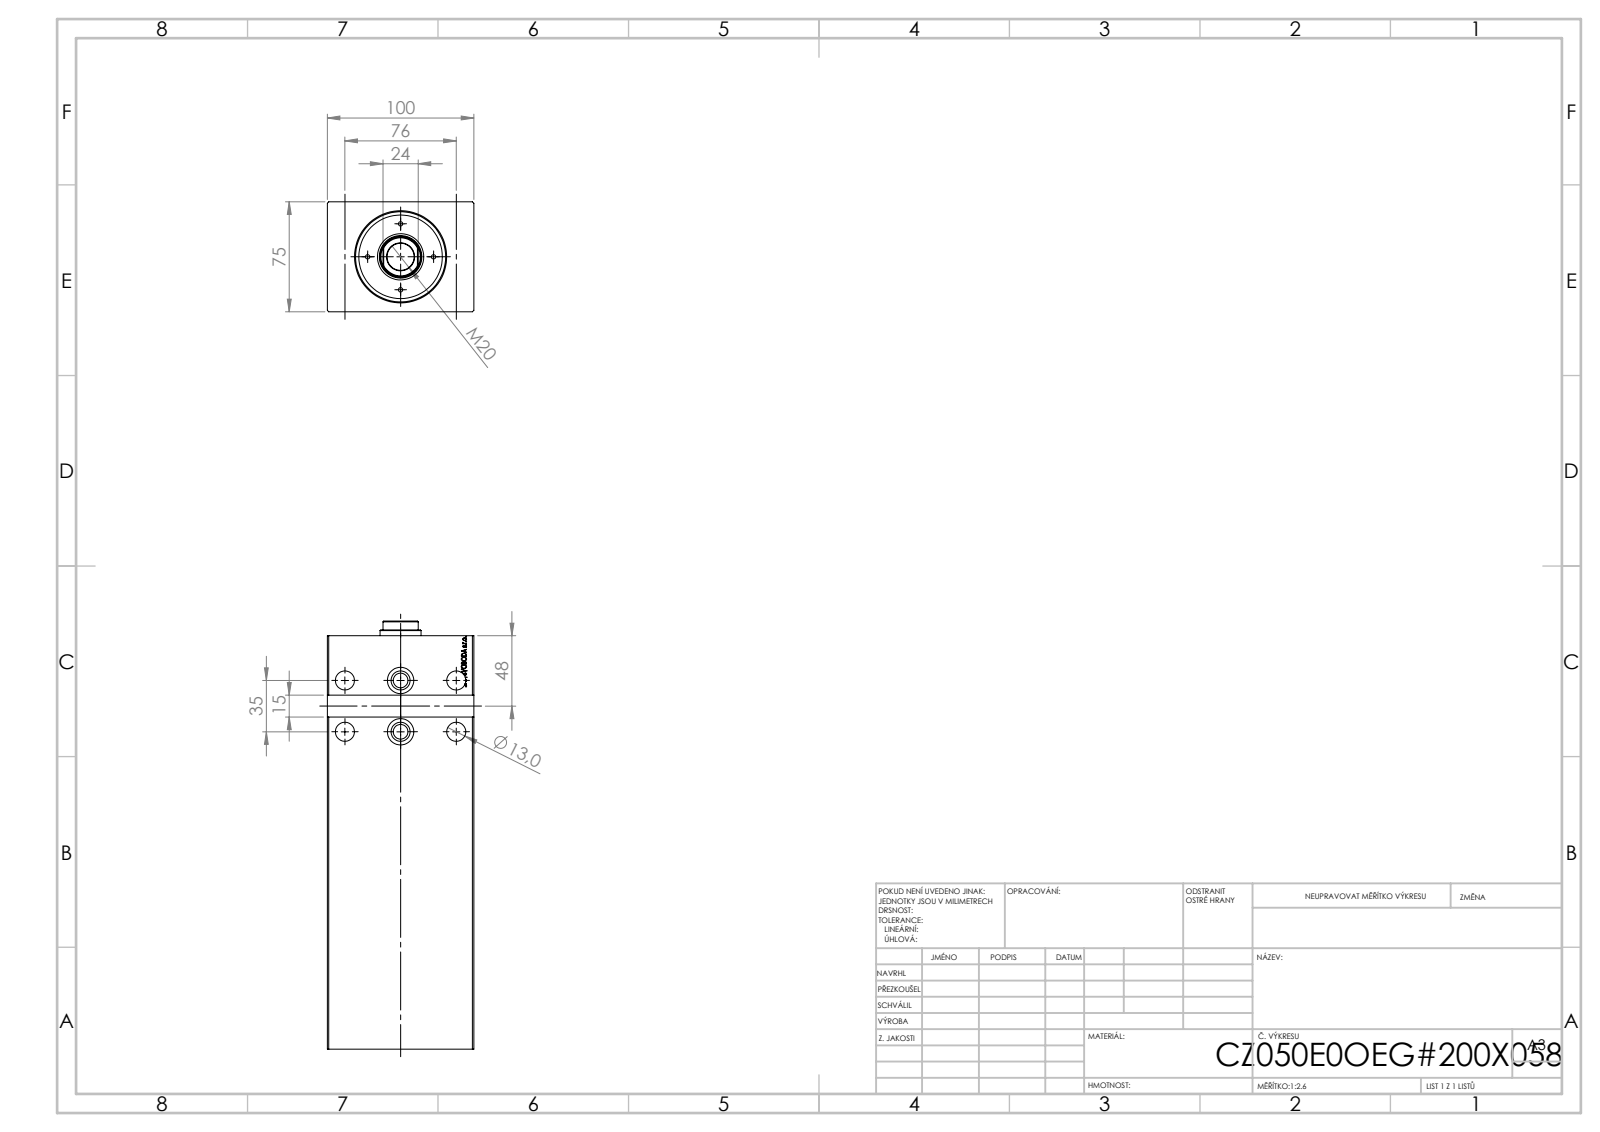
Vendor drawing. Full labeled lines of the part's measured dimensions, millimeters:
STEP written by: SolidWorks 2019 (CONFIG_CONTROL_DESIGN)
Units: millimetres
Bodies: 1 solid, 775 faces (375 planar, 30 cylindrical, 370 other)
Overall size (bounding box): 282 × 100 × 75
Volume: 1 541 000 mm³ · Surface area: 167 119 mm²
Round holes (diameter × count): ⌀13 ×4, ⌀8 ×2, ⌀10 ×2, ⌀18 ×2, ⌀36 ×1, ⌀50 ×1, ⌀61.5 ×1
Round bosses / shafts (diameter × count): ⌀13 ×2
Main face-to-face distances: 75, 100, 282, 264.2, 17.8, 2, 73, 281.8, 17.6, 10
Hole centre spacings: 38, 51.66, 35, 76, 83.67, 19.14, 21.03, 33.71
